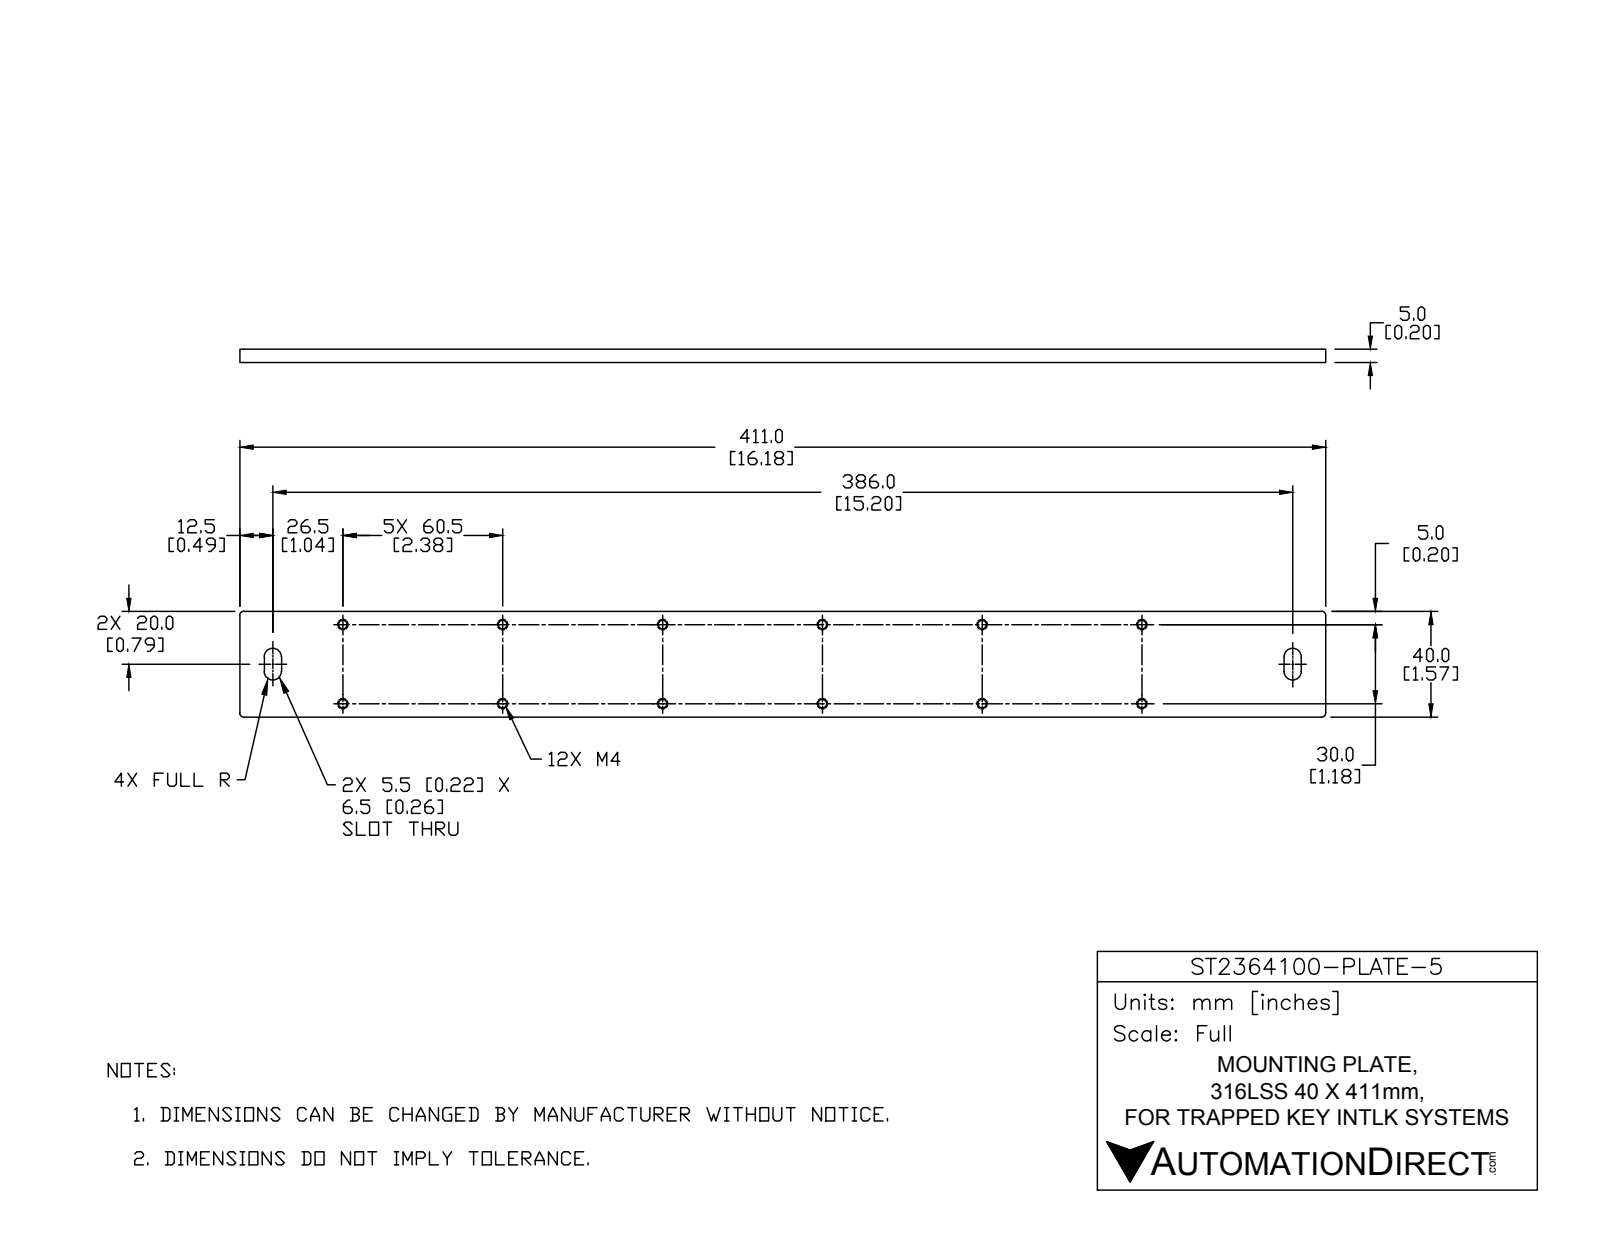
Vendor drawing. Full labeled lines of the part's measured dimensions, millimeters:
Part name (STEP PRODUCT): ST2364100-PLATE-5
STEP written by: SolidWorks 2017 (AUTOMOTIVE_DESIGN)
Units: millimetres
Bodies: 1 solid, 62 faces (10 planar, 36 cylindrical, 16 other)
Overall size (bounding box): 411 × 40 × 5
Volume: 80 900 mm³ · Surface area: 37 420 mm²
Round holes (diameter × count): ⌀3.3 ×12
Partial cylindrical surfaces — rounded edges, fillets, slot ends (radius × count): R0.2 ×8, R0.5 ×8, R2 ×4, R3.3 ×4
Main face-to-face distances: 5, 40, 411, 9.2, 15.7, 395.2, 401.8, 6.5, 386, 392.5
Hole centre spacings: 60, 67.1, 120, 123.7, 30, 180, 182.5, 240
